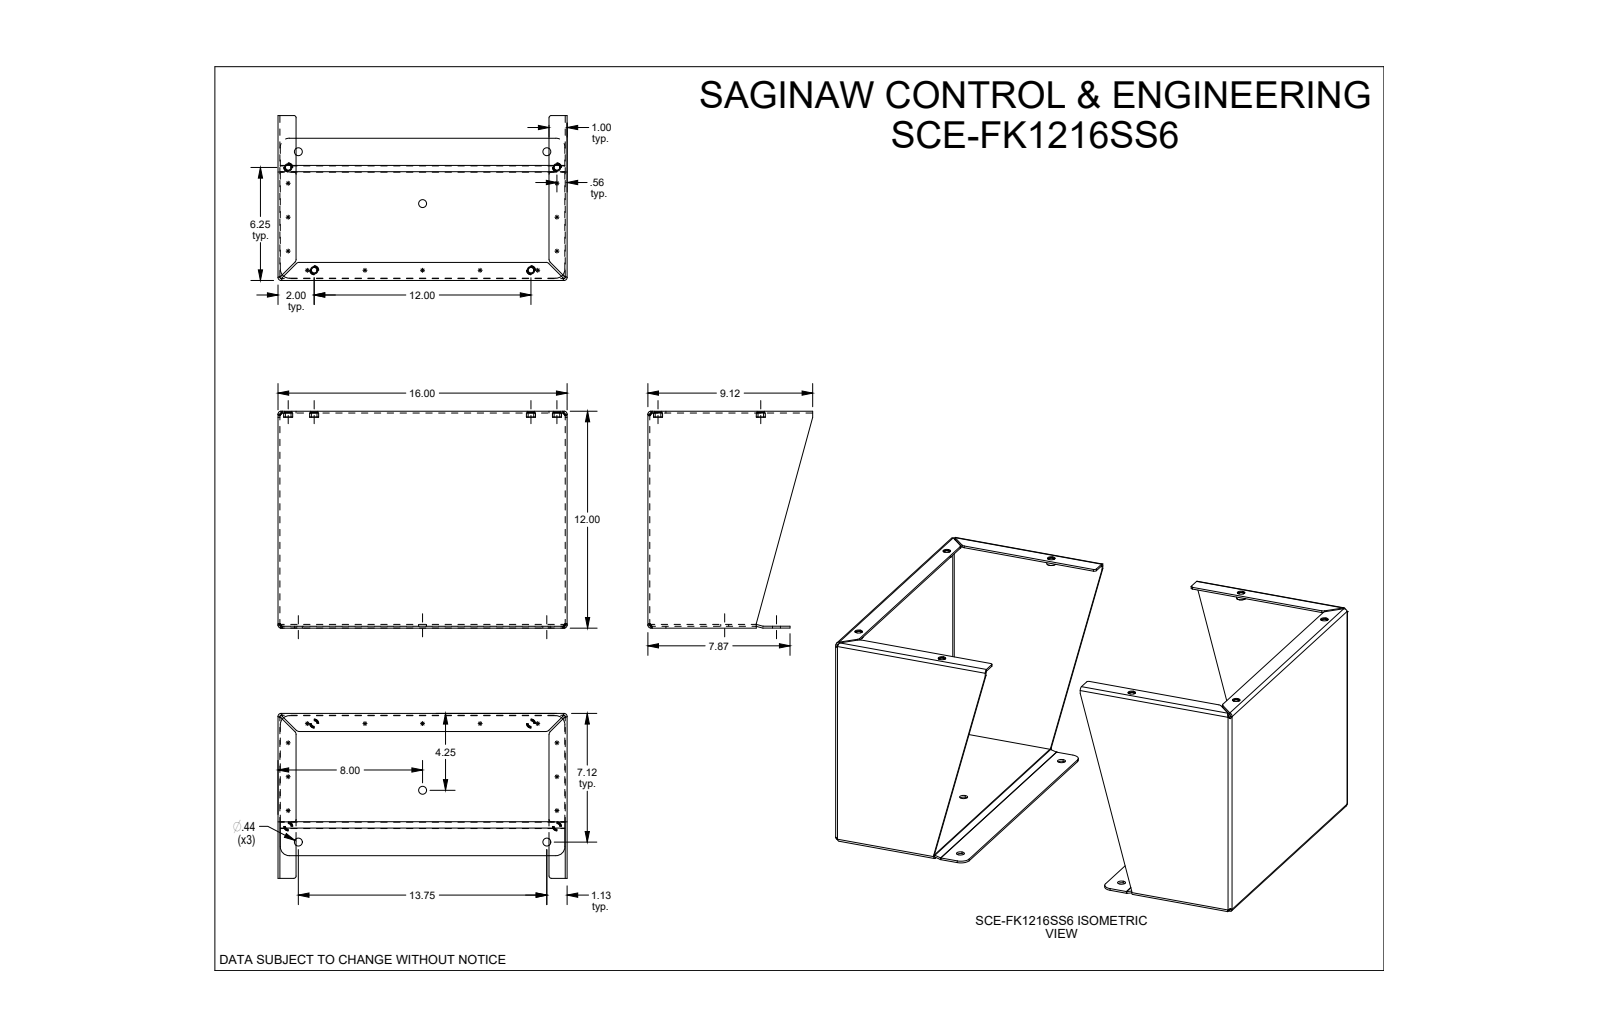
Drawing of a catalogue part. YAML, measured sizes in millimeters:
part_name: "SCE-FK1216SS6"
step_written_by: "SolidWorks 2019 (CONFIG_CONTROL_DESIGN)"
units: millimeters
bodies: {solids: 12, faces: 286, planar: 120, cylindrical: 110, other: 56}
overall_size: [609.6, 406.4, 304.8]
volume: 1842000
surface_area: 1416000
round_holes:
  - {diameter: 7.9, count: 8}
  - {diameter: 10.5, count: 8}
  - {diameter: 11.1, count: 6}
round_bosses_or_shafts:
  - {diameter: 12.7, count: 8}
  - {diameter: 10.5, count: 8}
partial_cylinders:
  - {radius: 4.2, count: 16}
  - {radius: 1.6, count: 12}
  - {radius: 3.2, count: 8}
  - {radius: 5.6, count: 8}
  - {radius: 12.7, count: 8}
  - {radius: 1.6, count: 6}
face_to_face_distances: [2.6, 607, 403.8, 604.3, 609.6, 401.1, 406.4, 299.5, 302.2, 2.6]
hole_center_spacings: [26.3, 149, 168, 178.9, 189.2, 195.6, 270.4, 365.3]
